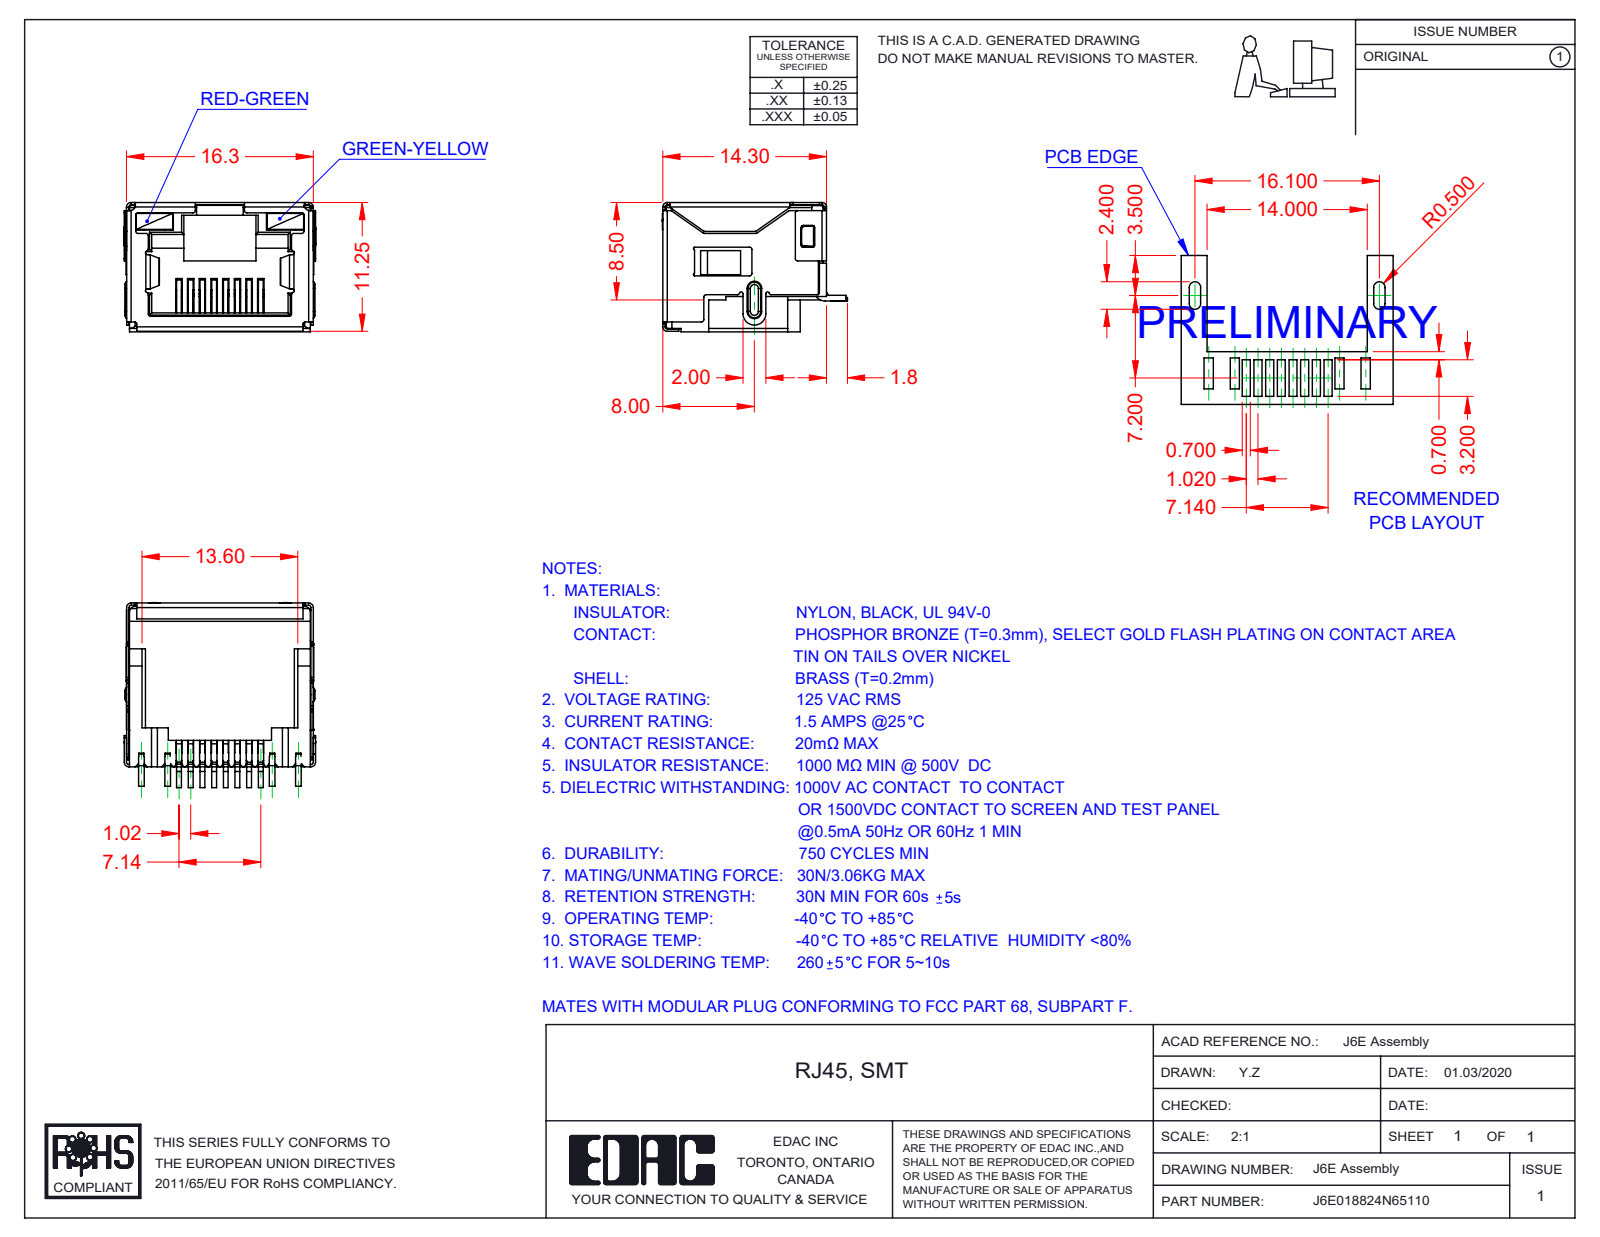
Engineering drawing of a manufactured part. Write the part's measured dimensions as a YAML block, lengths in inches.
part_name: "6E Insulator_LED; 6E LED RH_5-Green-Yellow; 6E LED LH_6-Red-Green; 6E Shield_LED (+2 more)"
step_written_by: "SolidWorks 2016 (CONFIG_CONTROL_DESIGN)"
units: inches
bodies: {solids: 12, faces: 1500, planar: 1099, cylindrical: 351, other: 50}
overall_size: [0.659, 0.636, 0.445]
volume: 0.068
surface_area: 6.27
partial_cylinders:
  - {radius: 0.008, count: 82}
  - {radius: 0.01, count: 17}
  - {radius: 0.016, count: 13}
  - {radius: 0.02, count: 13}
  - {radius: 0.004, count: 10}
  - {radius: 0.006, count: 7}
  - {radius: 0.012, count: 4}
  - {radius: 0.039, count: 3}
face_to_face_distances: [0.435, 0.632, 0.634, 0.624, 0.437, 0.445, 0.094, 0.028, 0.388, 0.019]
